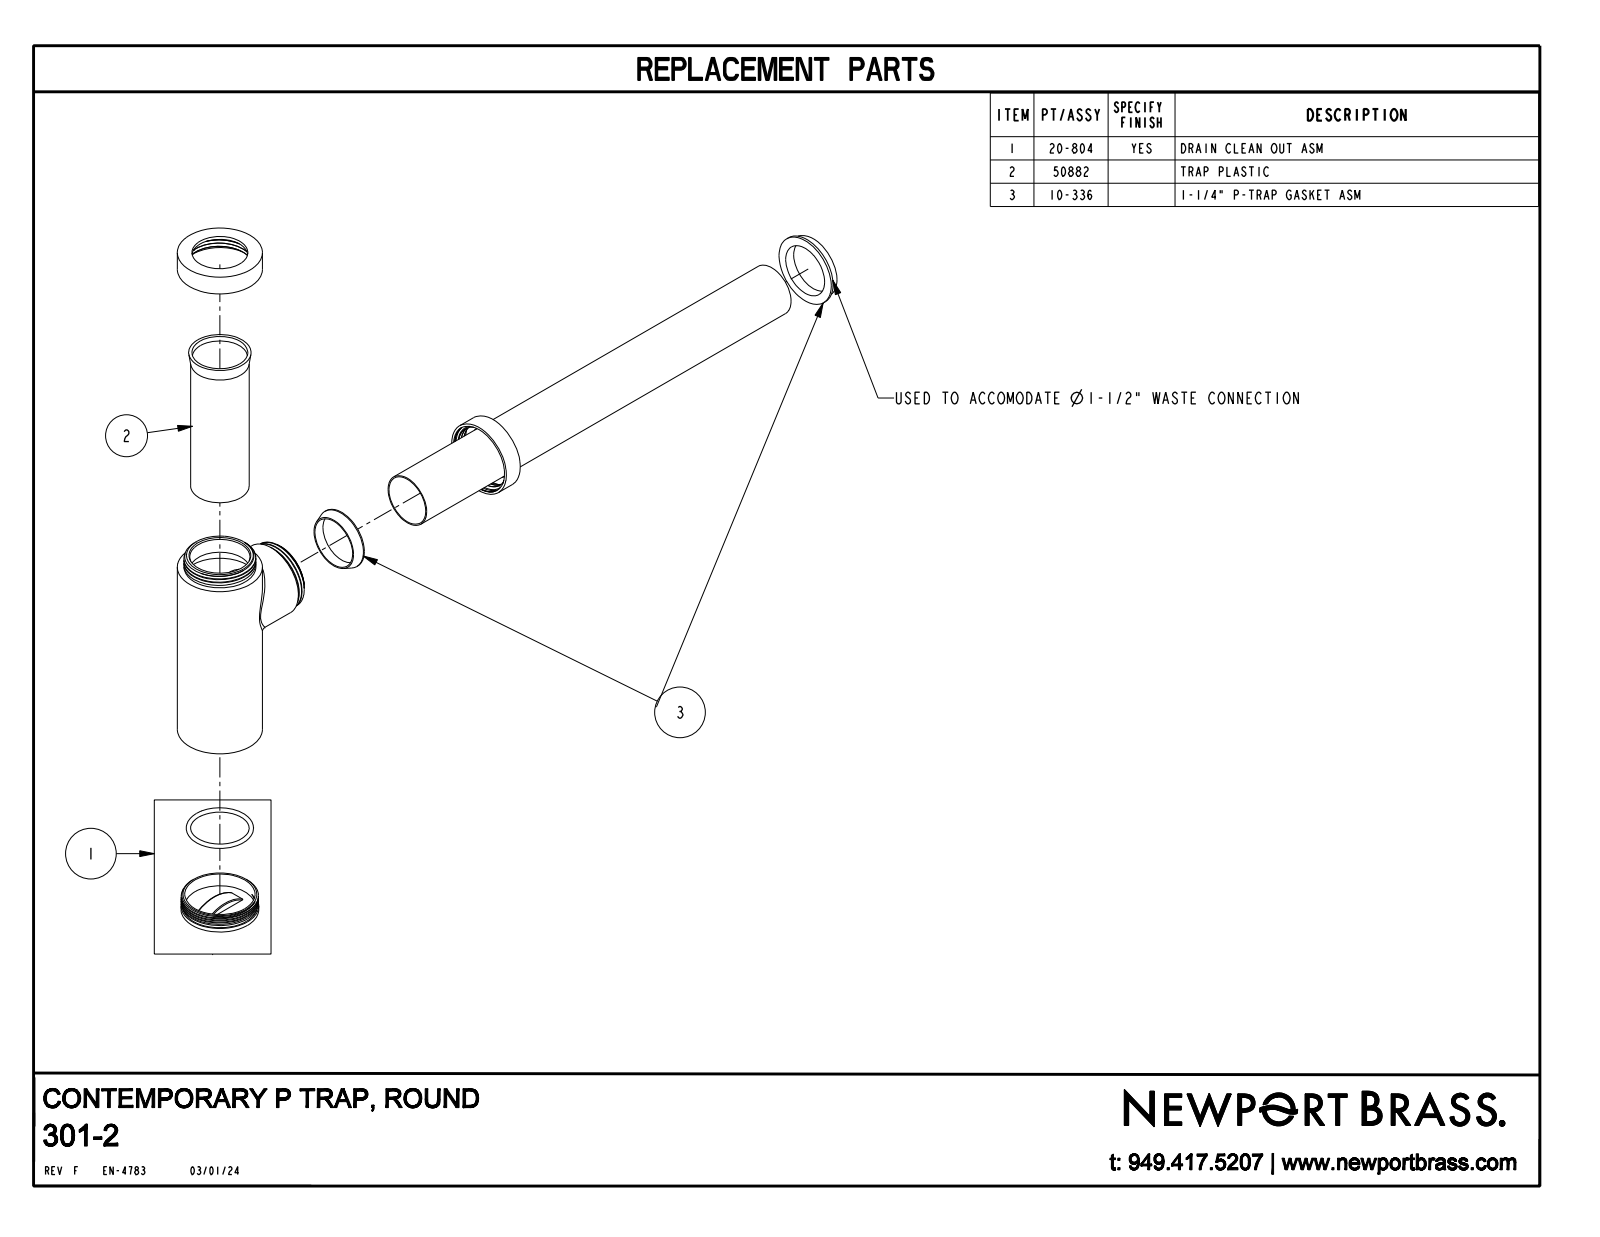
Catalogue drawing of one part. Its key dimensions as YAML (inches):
part_name: "301-2"
step_written_by: "CREO PARAMETRIC BY PTC INC, 2018500 (CONFIG_CONTROL_DESIGN)"
units: inches
bodies: {solids: 2, faces: 164, planar: 50, cylindrical: 80, other: 34}
overall_size: [14.007, 5.06, 2.56]
volume: 26.36
surface_area: 262.2
round_holes:
  - {diameter: 1.19, count: 2}
  - {diameter: 1.28, count: 2}
  - {diameter: 1.23, count: 1}
  - {diameter: 1.25, count: 1}
  - {diameter: 1.26, count: 1}
  - {diameter: 1.73, count: 1}
  - {diameter: 1.85, count: 1}
  - {diameter: 2.52, count: 1}
round_bosses_or_shafts:
  - {diameter: 2.56, count: 1}
  - {diameter: 1.95, count: 1}
  - {diameter: 1.78, count: 1}
  - {diameter: 1.77, count: 1}
  - {diameter: 1.75, count: 1}
  - {diameter: 1.715, count: 1}
  - {diameter: 1.685, count: 1}
  - {diameter: 1.679, count: 1}
partial_cylinders:
  - {radius: 0.1, count: 2}
  - {radius: 0.98, count: 1}
  - {radius: 1.02, count: 1}
face_to_face_distances: [0.02, 5.06, 0.1, 7.9, 7.88, 4.96, 3.38, 1.68, 4.9, 3.28]
